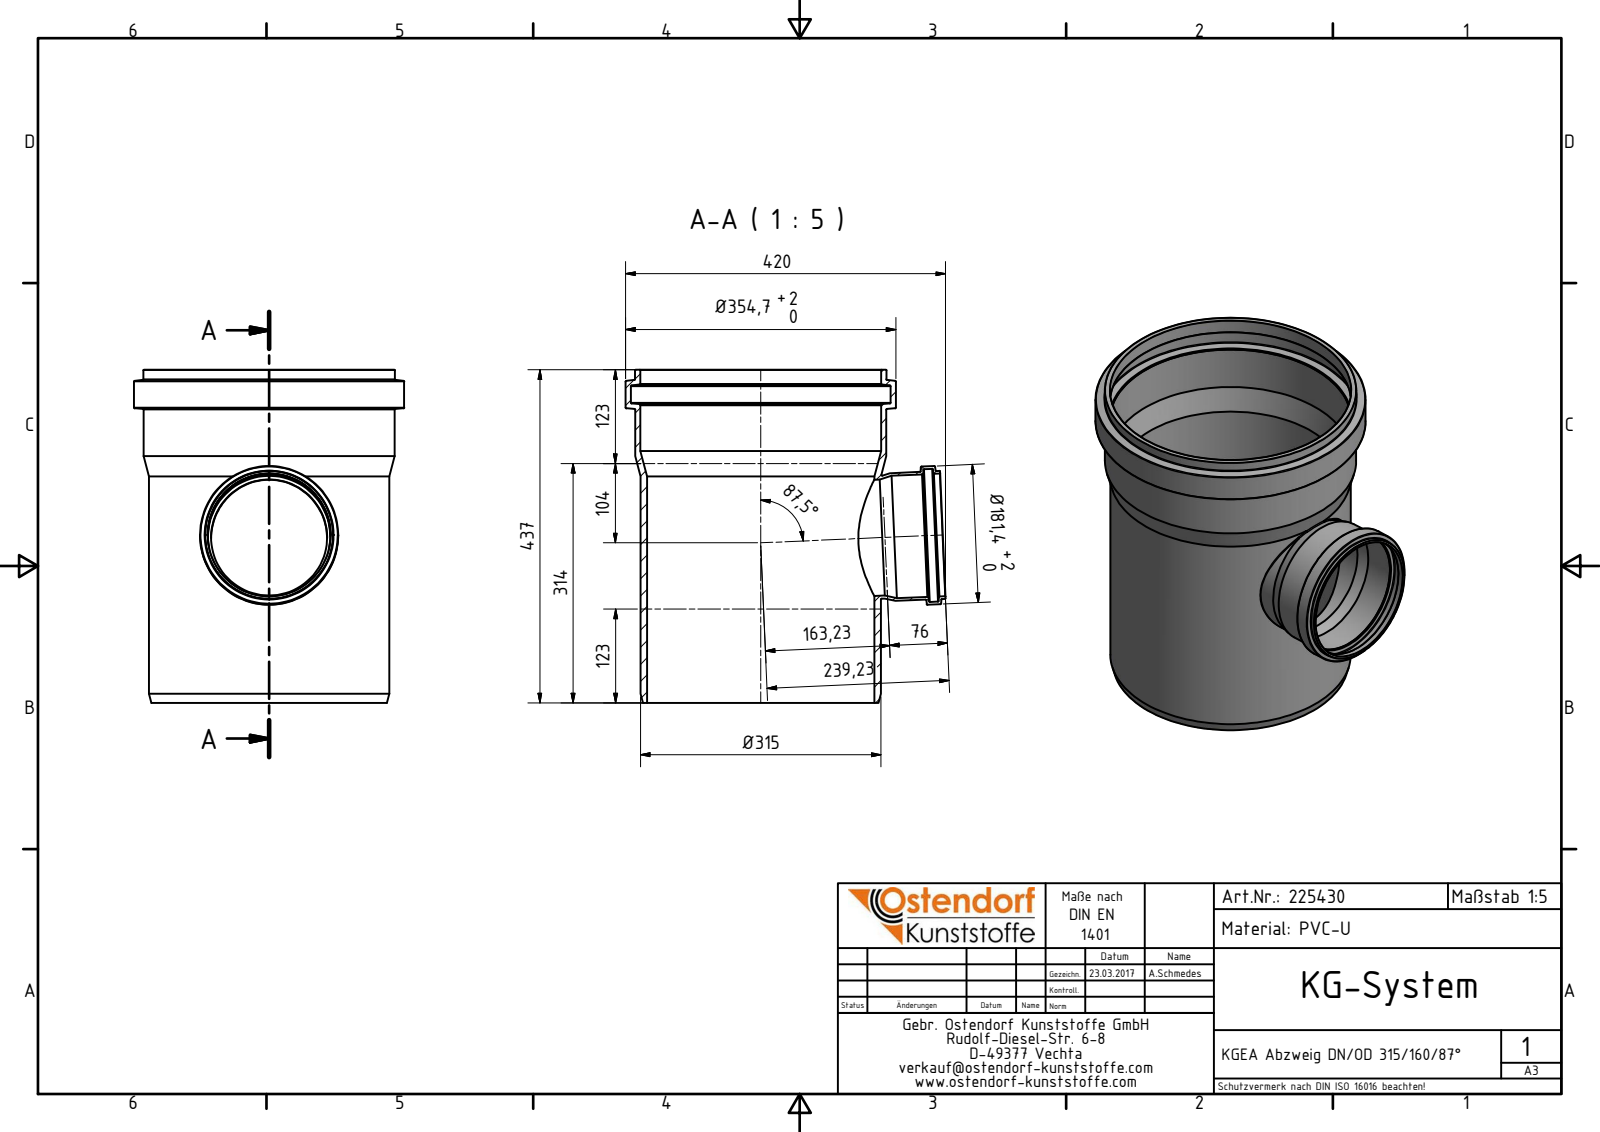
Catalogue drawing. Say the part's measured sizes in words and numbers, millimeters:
The part is named "225430 KGEA Abzweig DN_OD 315_160_87°". Its 3-D file was written by "Autodesk Inventor 2016 (AUTOMOTIVE_DESIGN)". It is 1 solid with 60 faces: 5 planar, 18 cylindrical and 37 other. Overall it measures 437 by 420 by 354.7 millimeters. Its volume is 3 711 000 cubic millimeters and its surface area 991 438 square millimeters. Round holes: 2 of diameter 161.1, 1 of diameter 152.3, 1 of diameter 160.7, 1 of diameter 174.4, 1 of diameter 298.2, 1 of diameter 316, 1 of diameter 316.3, 1 of diameter 340.9. Round bosses or shafts: 1 of diameter 354.7, 1 of diameter 330.1, 1 of diameter 329.8, 1 of diameter 315.6, 1 of diameter 181.4, 1 of diameter 168.1, 1 of diameter 167.7, 1 of diameter 160.3. The main face-to-face distances are 437, 390.44, 46.56, 23.61.
